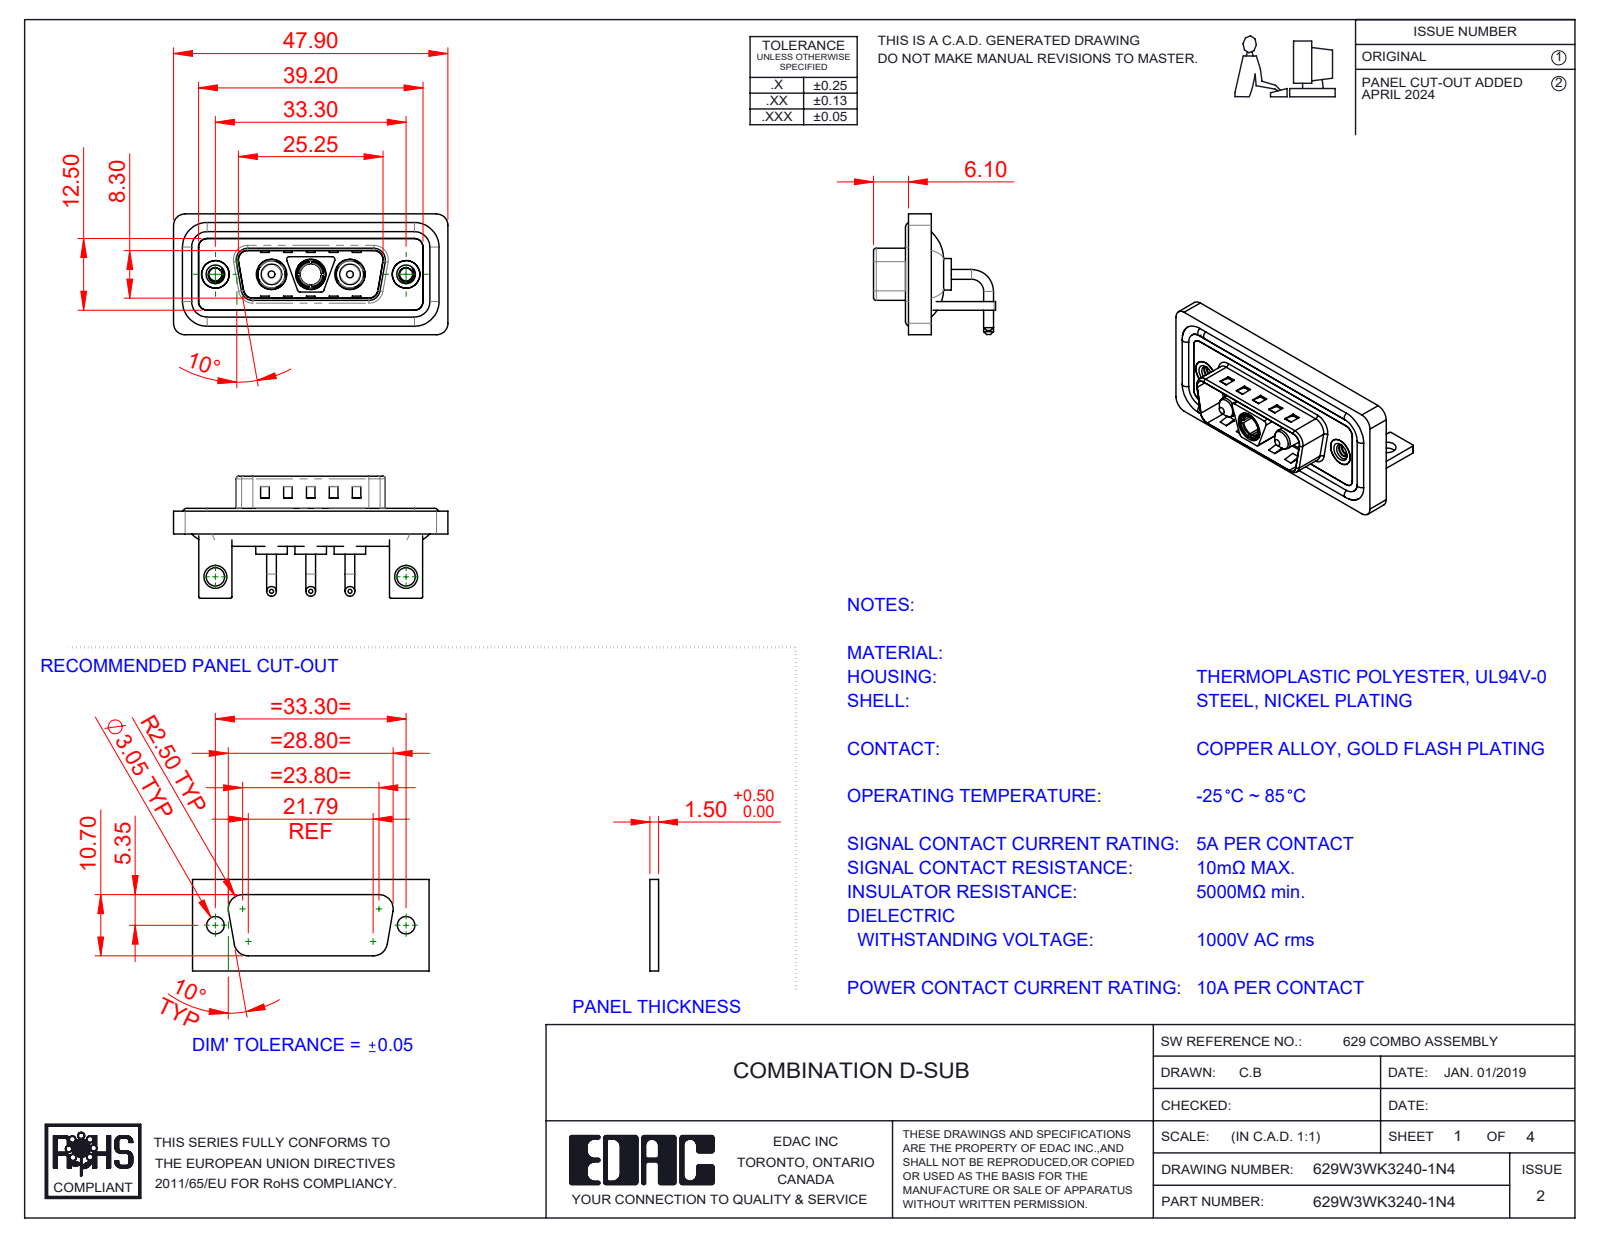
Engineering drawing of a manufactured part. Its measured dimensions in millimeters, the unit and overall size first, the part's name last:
Units: millimetres
Overall size (bounding box): 47.9 × 21.3 × 21.1
Round holes (diameter × count): ⌀4.85 ×3, ⌀5.3 ×3, ⌀2.26 ×2, ⌀3.2 ×2, ⌀4 ×2, ⌀4.8 ×2, ⌀5 ×2, ⌀3.7 ×1
Round bosses / shafts (diameter × count): ⌀1.7 ×6, ⌀1.6 ×4, ⌀5.5 ×3, ⌀5.2 ×3, ⌀4.75 ×3, ⌀3.75 ×3, ⌀4.9 ×2, ⌀3.6 ×2
Partial cylindrical surfaces — rounded edges, fillets, slot ends (radius × count): R2 ×21, R1.5 ×18, R0.25 ×16, R0.5 ×13, R1.6 ×8, R0.6 ×4, R0.65 ×4, R0.9 ×4
Main face-to-face distances: 0.4, 1.5, 0.8, 2.9, 1.1, 2.1, 3.7, 1.6, 1.2, 4.5
Hole centre spacings: 6.85, 9.8, 16.65, 23.5, 33.3, 13.7
Volume: 5 986 mm³ · Surface area: 9 848 mm²
Bodies: 15 solids, 661 faces (251 planar, 274 cylindrical, 136 other)
Part name (STEP PRODUCT): 629Combo Threaded Rivet_3; 629W3WK3240-1N4; 629Combo Shell Rear_15 Contacts; 629Combo Shell Front_15 Contacts (+5 more)
STEP written by: SolidWorks 2023 (CONFIG_CONTROL_DESIGN)
